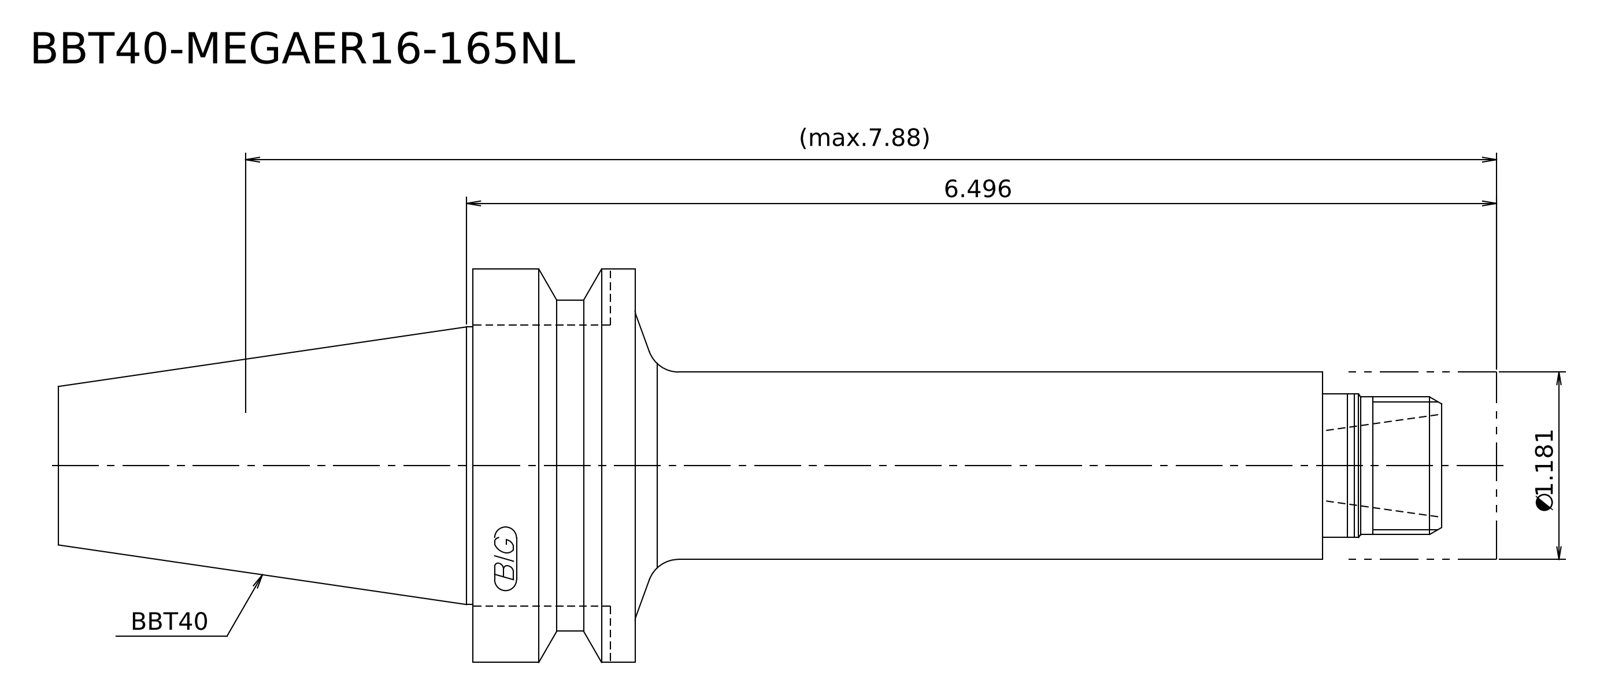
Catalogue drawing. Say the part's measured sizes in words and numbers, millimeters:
Its 3-D file was written by "Kubotek KeyCreator 2011 V10.0.2 (22737) (automotive_design)". It is 2 solids with 21 faces: 7 planar, 8 cylindrical and 6 other. Overall it measures 230.4 by 63 by 63 millimeters. Its volume is 246 993 cubic millimeters and its surface area 33 581 square millimeters. Round bosses or shafts: 1 of diameter 63, 1 of diameter 53, 1 of diameter 44.45, 1 of diameter 30, 1 of diameter 23, 1 of diameter 22. The main face-to-face distances are 26, 113, 139, 25, 138, 164, 230.4, 205.4, 92.4, 66.4.
